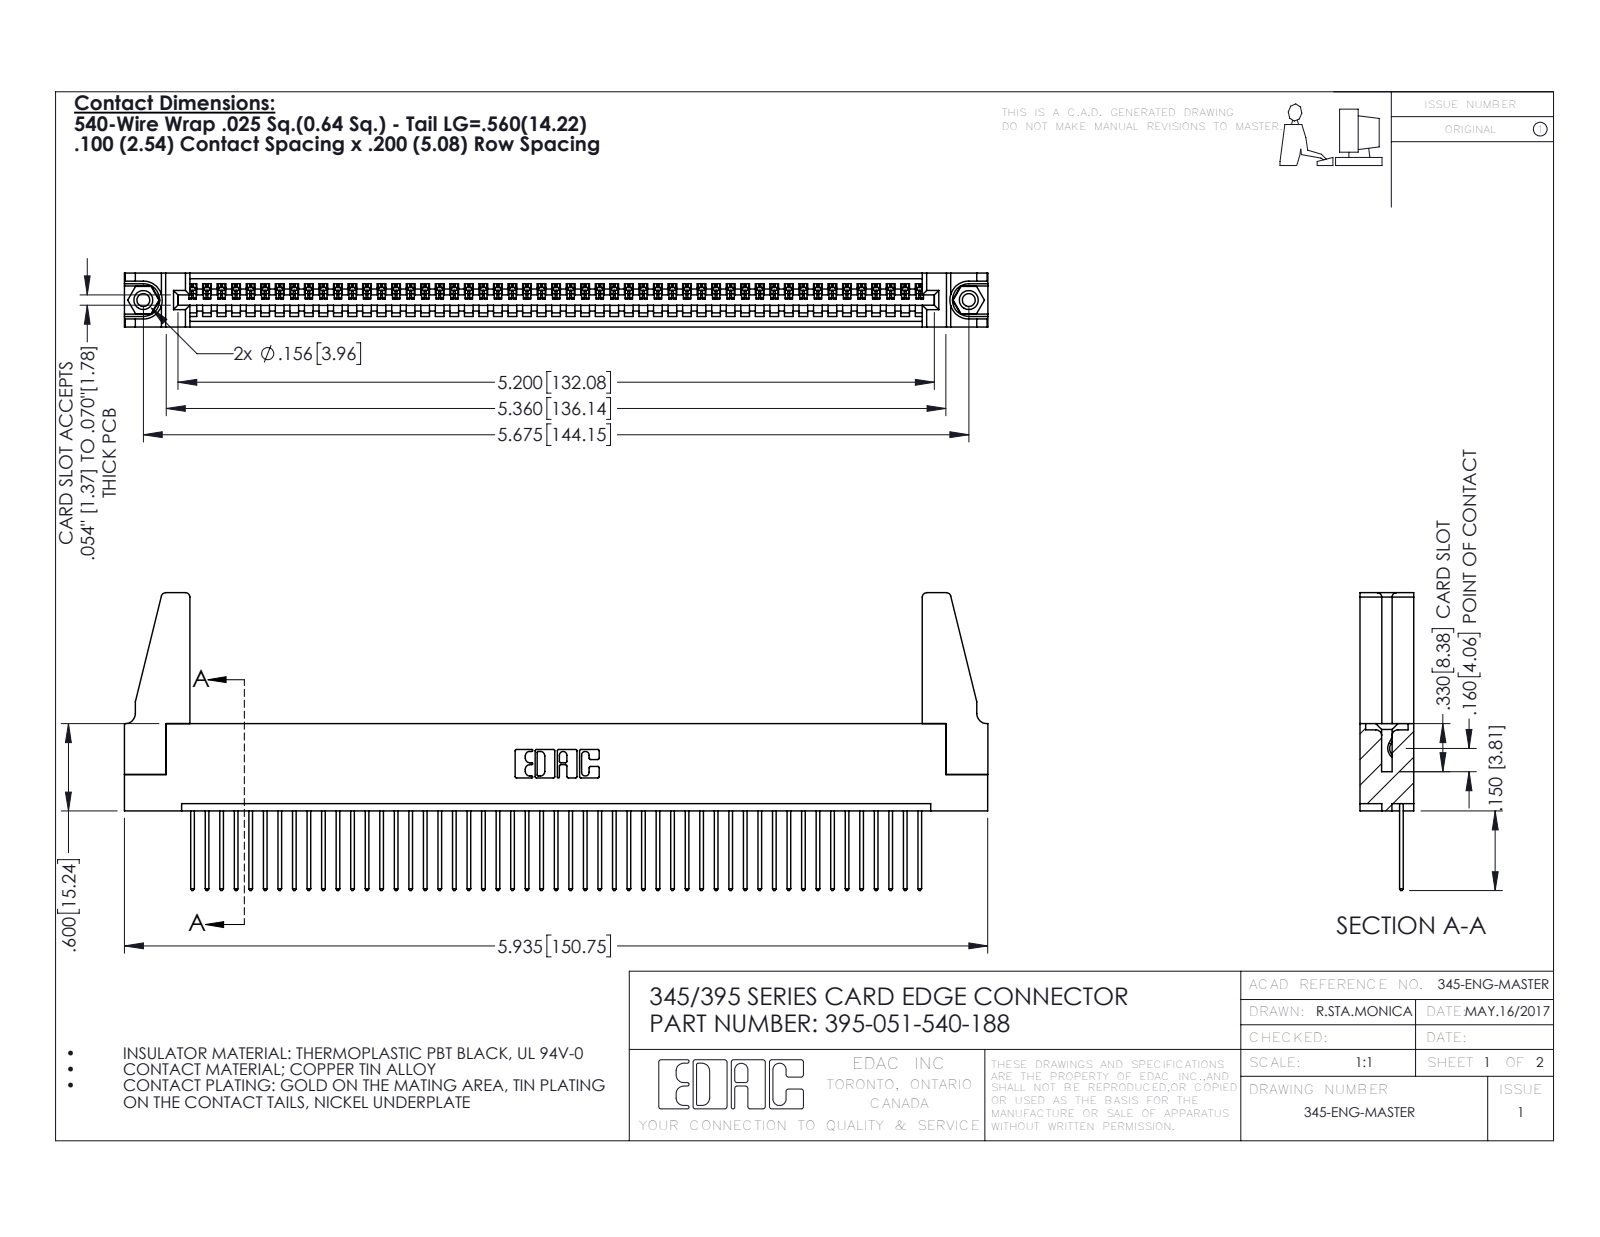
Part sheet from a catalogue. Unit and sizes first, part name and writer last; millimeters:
Units: millimetres
Overall size (bounding box): 150.8 × 52 × 9.4
Round holes (diameter × count): ⌀2.3 ×2, ⌀3.2 ×2, ⌀4 ×2, ⌀1.6 ×1
Round bosses / shafts (diameter × count): ⌀3.9 ×2
Partial cylindrical surfaces — rounded edges, fillets, slot ends (radius × count): R0.2 ×102, R0.3 ×102, R0.3 ×22, R0.8 ×8, R0.2 ×6, R0.8 ×6, R0.7 ×3, R0.8 ×2
Main face-to-face distances: 1.8, 7.6, 9.4, 2.5, 6.9, 0.6, 5.1, 5.7, 3.8, 1.8
Hole centre spacings: 6.9, 138.2, 144.1
Volume: 17 710 mm³ · Surface area: 22 970 mm²
Bodies: 56 solids, 3208 faces (2192 planar, 1000 cylindrical, 16 other)
Part name (STEP PRODUCT): 395-051-540-188; 345-292-001_345-293-140; 345 Part_Flush Mounting Lugs - 0.156 Dia-TH; 345-220-078_345-220-088 (+1 more)
STEP written by: SolidWorks 2016 (CONFIG_CONTROL_DESIGN)
